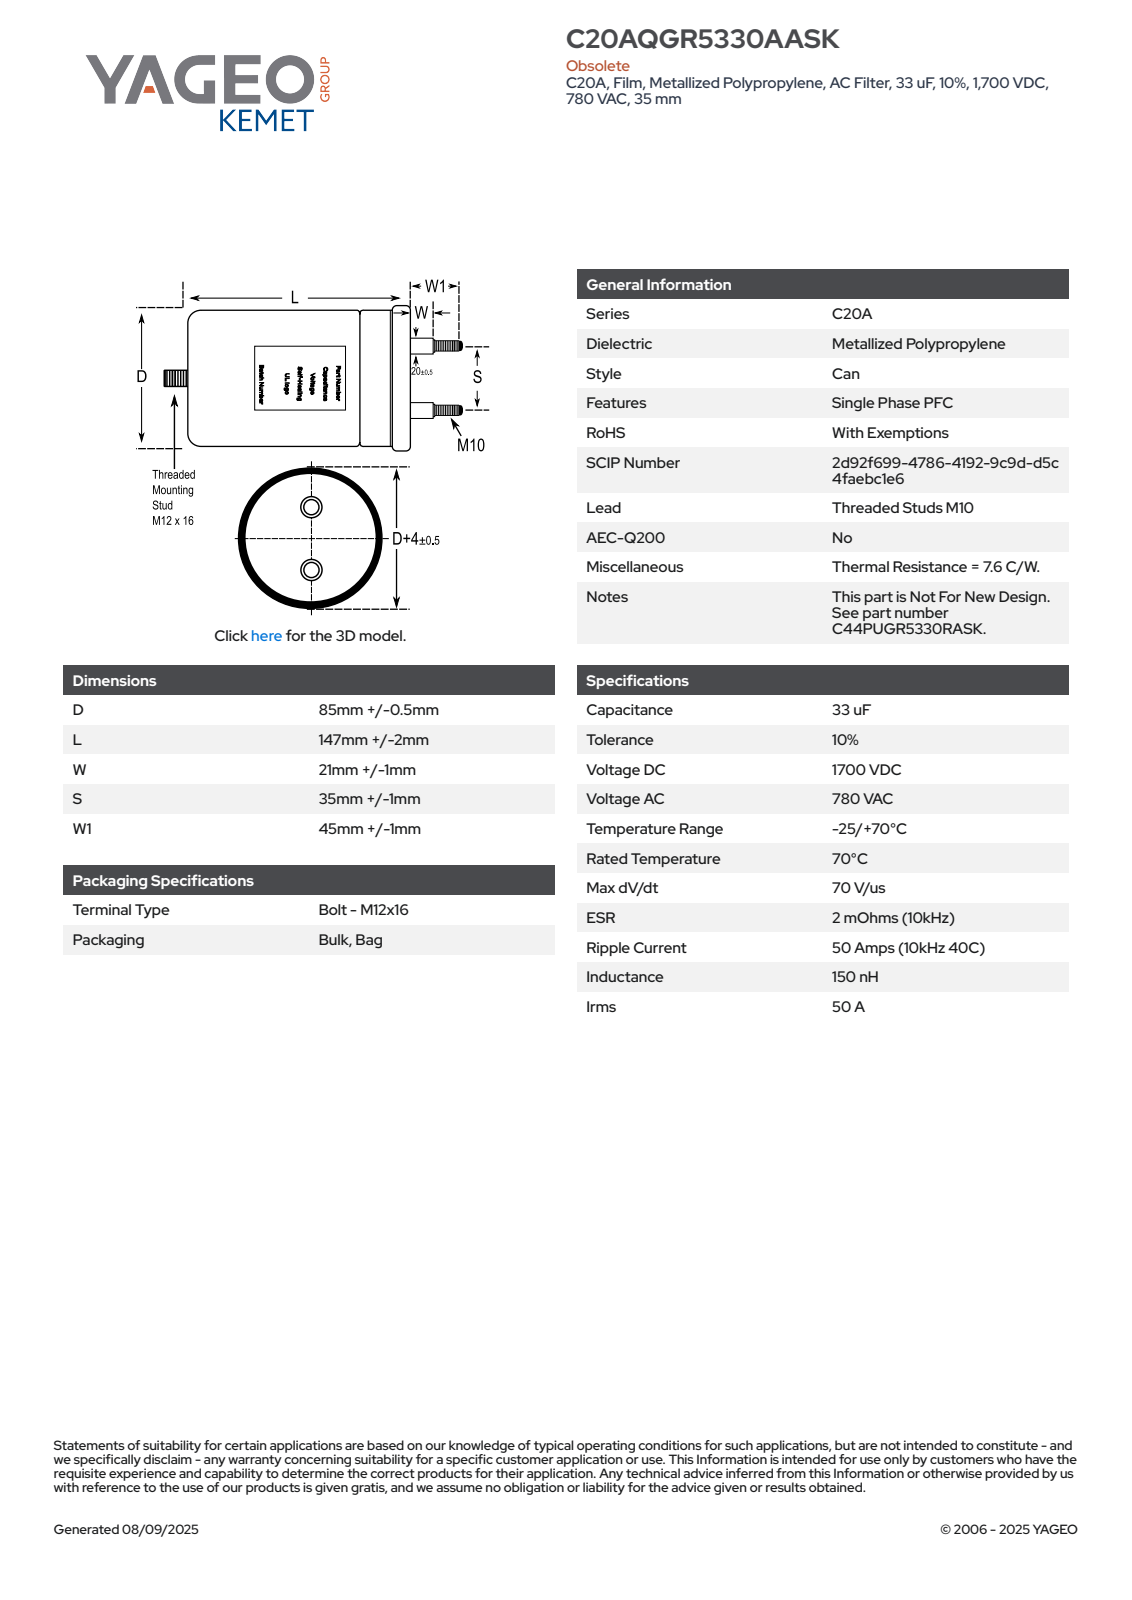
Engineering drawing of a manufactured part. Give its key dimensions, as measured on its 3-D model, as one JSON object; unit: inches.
{"part_name": "CFP_C44P_85X147_D85.5L149S35", "step_written_by": "SolidWorks 2014 (AUTOMOTIVE_DESIGN)", "units": "inches", "bodies": {"solids": 1, "faces": 105, "planar": 32, "cylindrical": 36, "other": 37}, "overall_size": [8.307, 3.543, 3.543], "volume_in3": 53.49, "surface_area_in2": 88.16, "round_bosses_or_shafts": [[0.472, 3], [0.807, 2], [0.394, 2], [3.543, 1], [3.366, 1]], "partial_cylinders_radius": [[1.683, 1]], "face_to_face_distances": [5.866, 6.693, 0.827, 5.678, 0.188, 1.015, 7.677, 1.999, 1.811, 0.984]}
